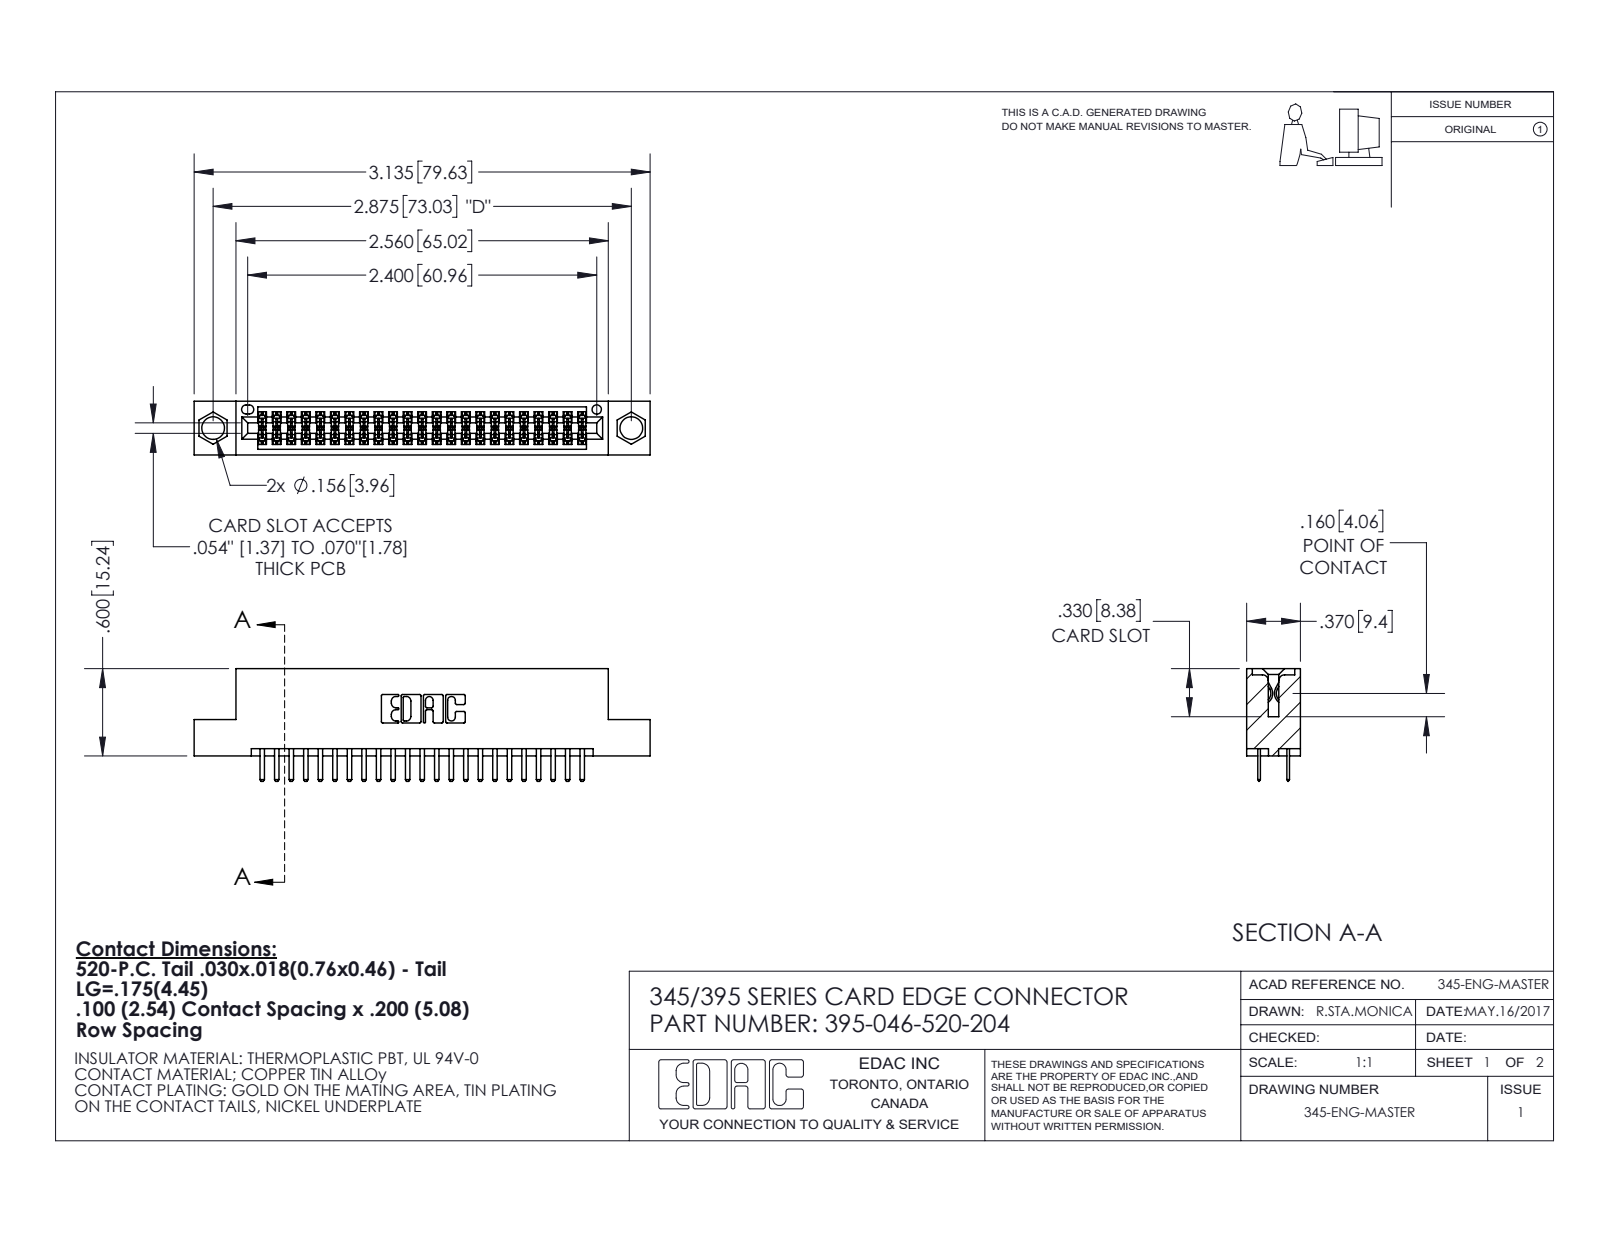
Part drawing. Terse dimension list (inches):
name: 345 Part_Flush Mounting Lugs - 0.156 Dia-TI; 345-292-001_345-293-120; 395-046-520-204
written by: SolidWorks 2020 (CONFIG_CONTROL_DESIGN)
unit: in
bodies: 47 solids, 2624 faces (1704 planar, 920 cylindrical, 0 other)
size: 3.135 × 0.775 × 0.37
volume: 0.454 in³; area: 16.16 in²
holes: 2× ⌀0.156, 1× ⌀0.064
rounds: 69× R0.006, 50× R0.01, 22× R0.01, 6× R0.007, 6× R0.031, 3× R0.026, 2× R0.014, 2× R0.019
face distances: 0.298, 0.072, 0.2, 0.37, 0.098, 0.272, 0.025, 0.225, 0.022, 0.072
hole spacings: 0.27, 2.641, 2.875
